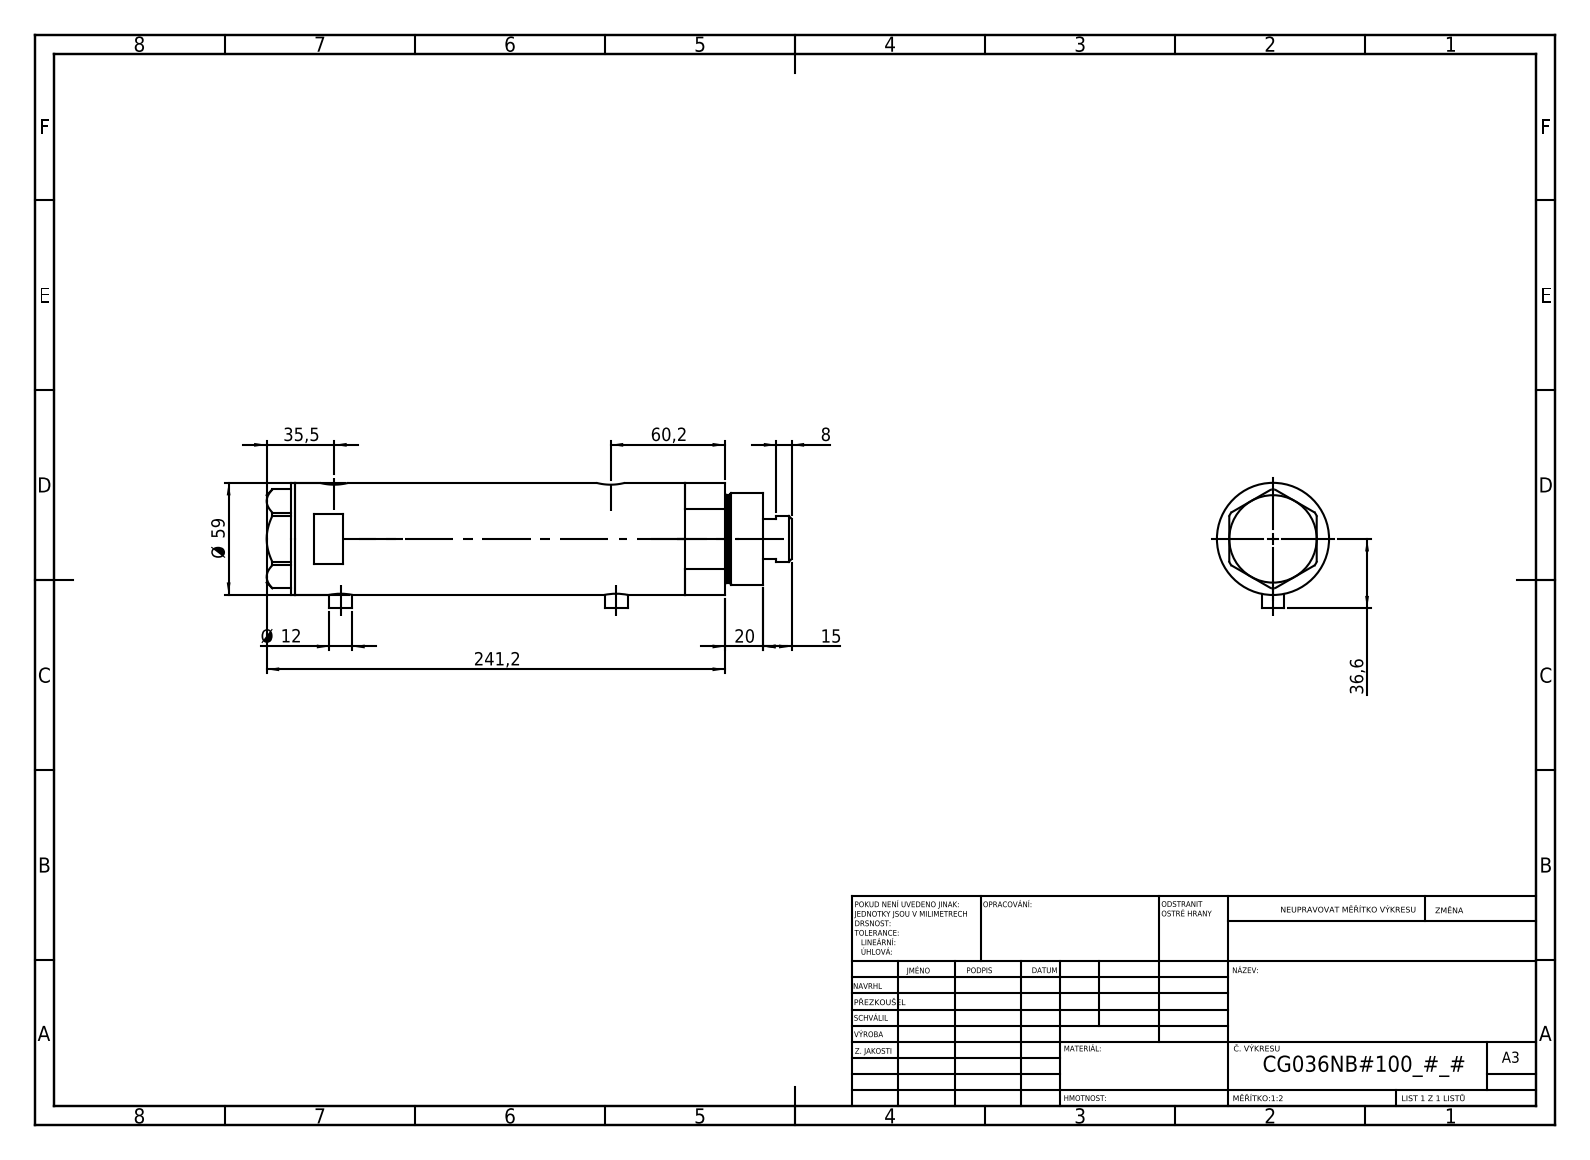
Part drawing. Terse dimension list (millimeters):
name: V270CG_VC; V270CG_FRONT; V270CG_BACK; V270CG_MIDDLE
written by: SolidWorks 2019 (CONFIG_CONTROL_DESIGN)
unit: mm
bodies: 4 solids, 120 faces (51 planar, 49 cylindrical, 20 other)
size: 276.2 × 66.1 × 59
volume: 629 802 mm³; area: 124 998 mm²
holes: 2× ⌀9.73, 2× ⌀12.5, 2× ⌀15, 1× ⌀8.5, 1× ⌀25, 1× ⌀26.5, 1× ⌀36, 1× ⌀40, 1× ⌀52
bosses: 2× ⌀12, 1× ⌀59, 1× ⌀48, 1× ⌀46, 1× ⌀24
face distances: 167.2, 23.5, 143.7, 15, 38.5, 182.2, 2, 261.2, 246.2, 222.7
hole spacings: 2.9, 3.5, 142, 144.9, 145.5, 148.4
